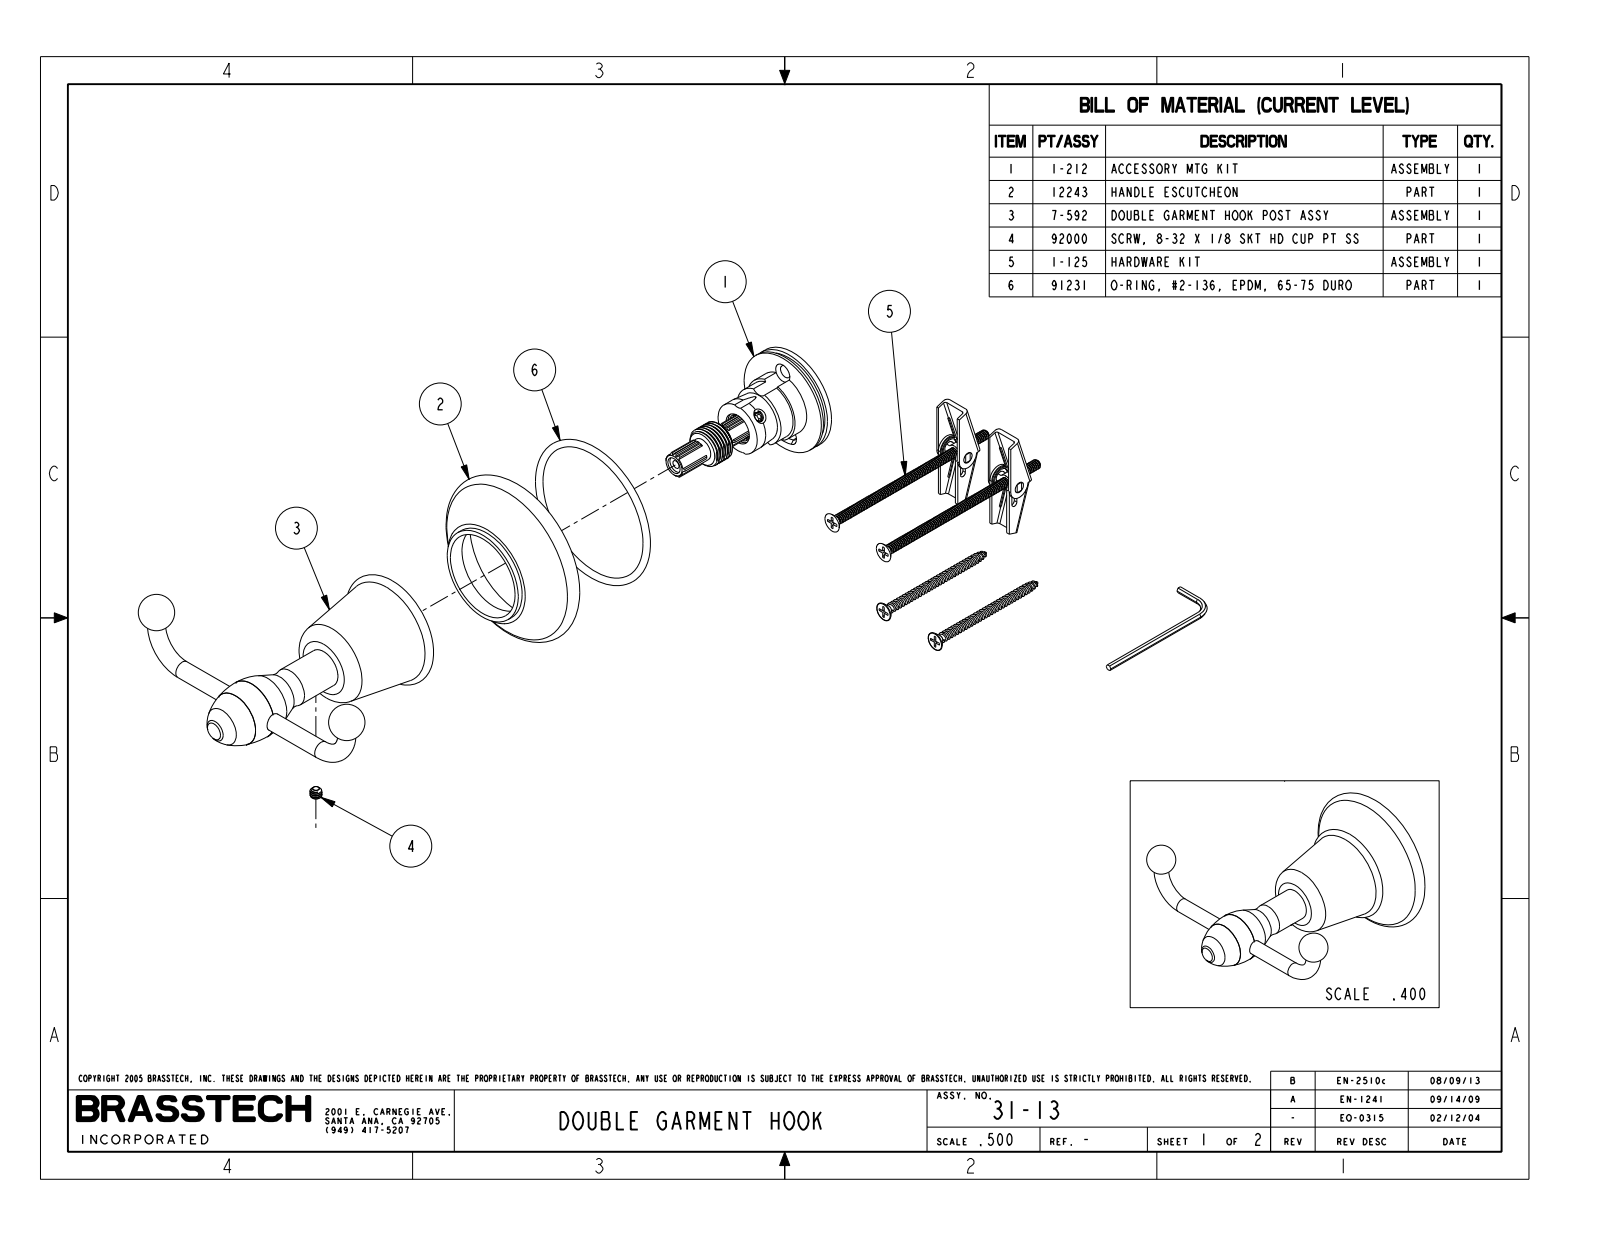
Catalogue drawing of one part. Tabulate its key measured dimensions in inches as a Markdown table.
| quantity | value |
| --- | --- |
| part name | 31-13_WEB |
| STEP written by | PRO/ENGINEER BY PARAMETRIC TECHNOLOGY CORPORATION, 2009300 (CONFIG_CONTROL_DESIGN) |
| units | inches |
| bodies | 0 solids, 59 faces (7 planar, 11 cylindrical, 41 other) |
| overall size | 4.2 × 4.153 × 2.35 |
| round bosses / shafts (diameter × count) | 0.553 × 1, 0.25 × 1, 0.164 × 1 |
| main face-to-face distances | 0.625, 1.975, 1.35, 0.825 |
